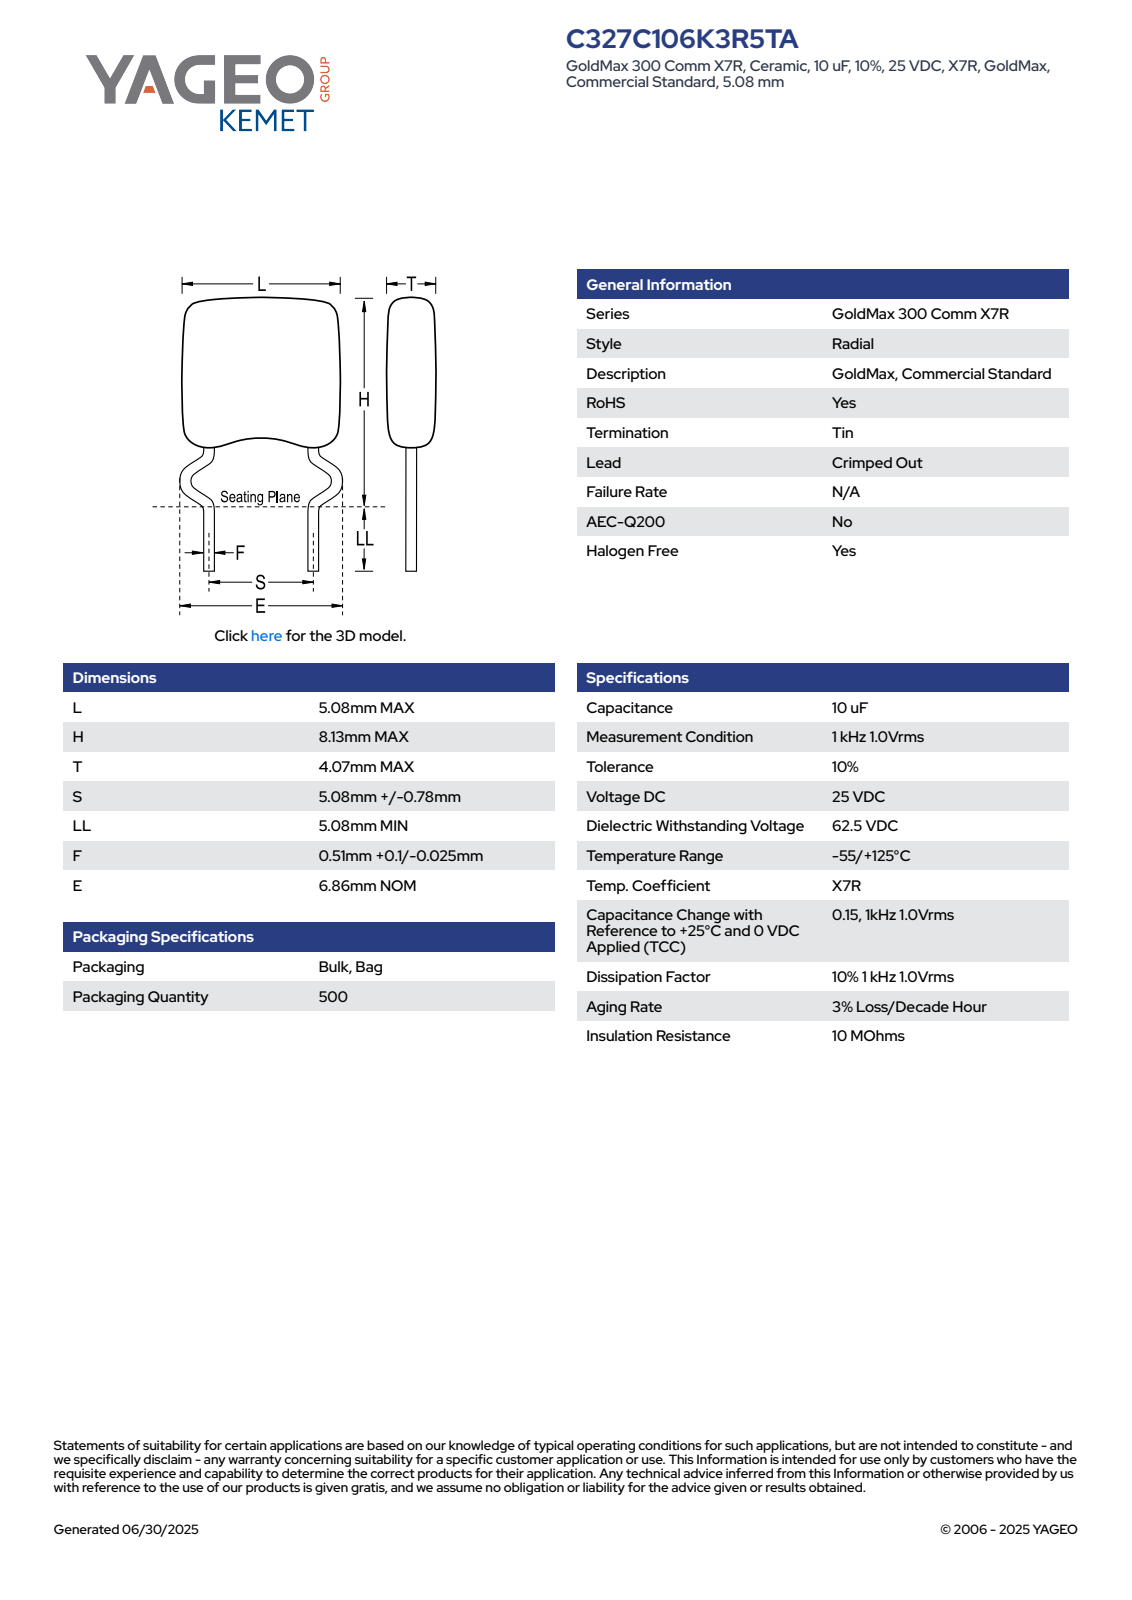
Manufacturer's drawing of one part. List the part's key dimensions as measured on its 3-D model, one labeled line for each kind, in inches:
Part name (STEP PRODUCT): CCR_RCCR_C327_L5.08H8.13T4.07S5.08LL5.08F0.51E6.86
STEP written by: SolidWorks 2014 (AUTOMOTIVE_DESIGN)
Units: inches
Bodies: 4 solids, 104 faces (66 planar, 16 cylindrical, 22 other)
Overall size (bounding box): 0.52 × 0.27 × 0.161
Volume: 0.006 in³ · Surface area: 0.242 in²
Round bosses / shafts (diameter × count): ⌀0.02 ×2
Partial cylindrical surfaces — rounded edges, fillets, slot ends (radius × count): R0.01 ×8, R0.03 ×4
Main face-to-face distances: 0.16, 0.2, 0.202, 0.161, 0.319, 0.52, 0.088, 0.114, 0.032, 0.432
